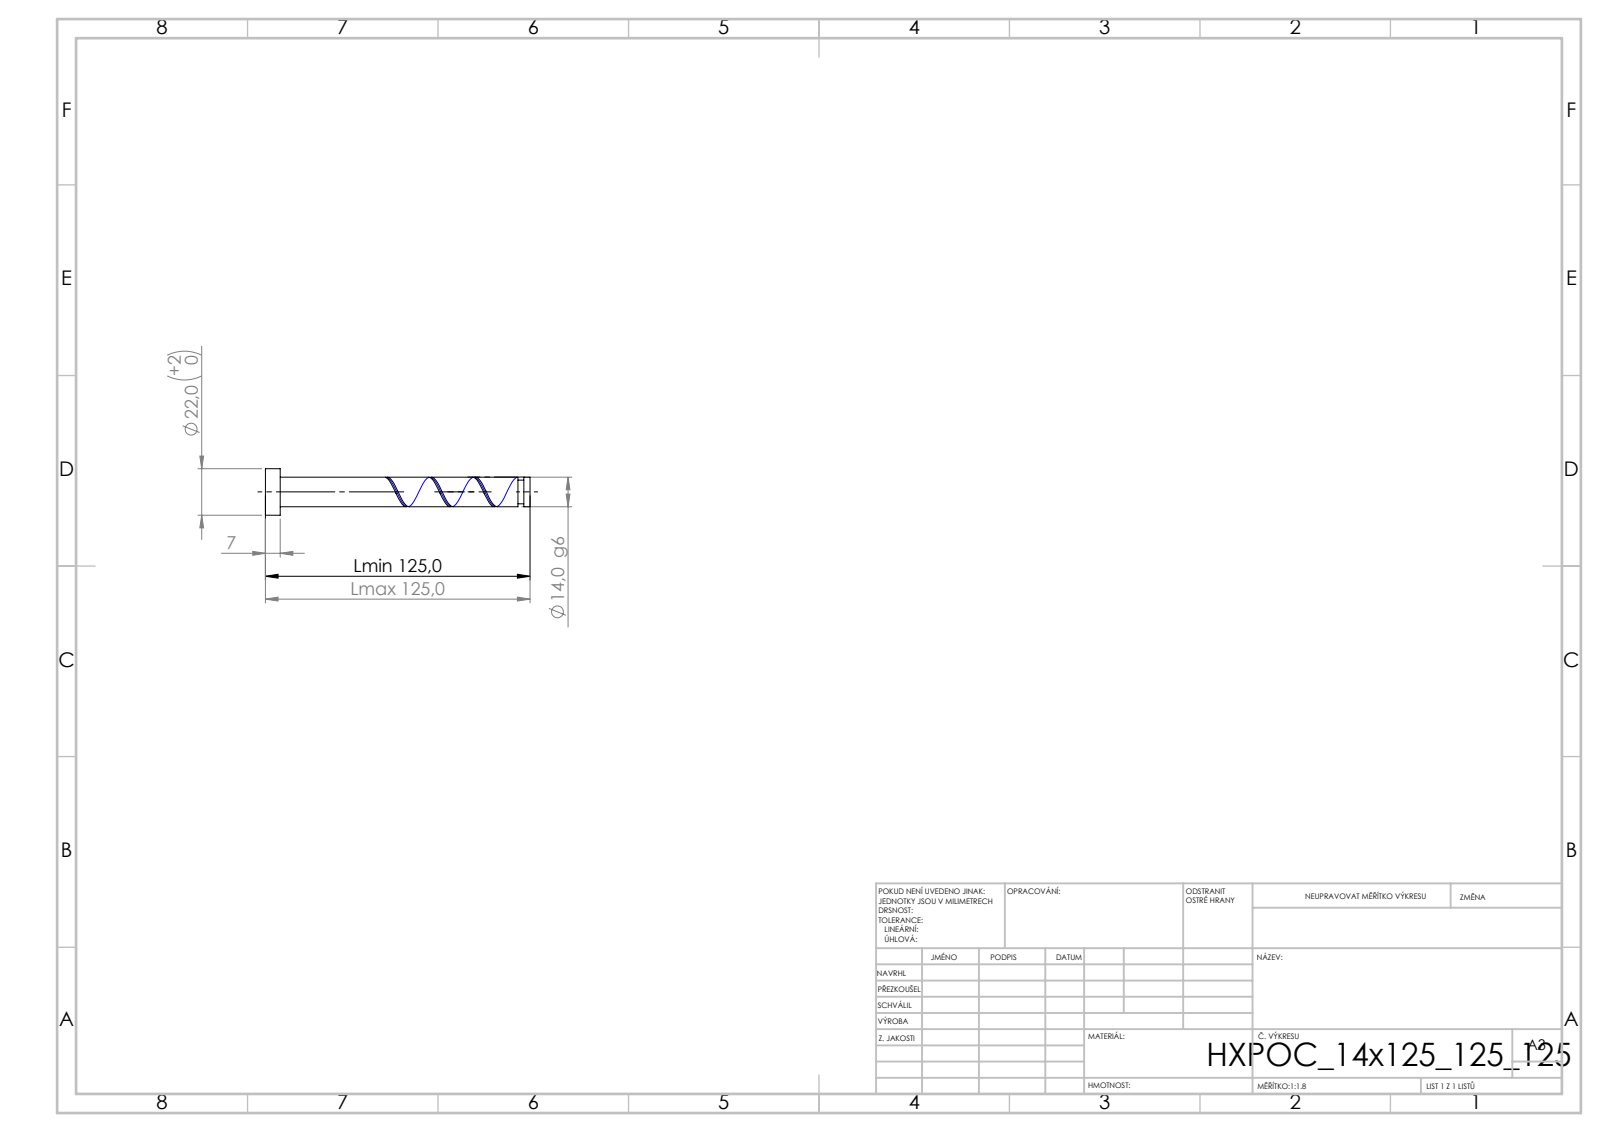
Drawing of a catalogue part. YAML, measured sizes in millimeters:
step_written_by: "SolidWorks 2019 (CONFIG_CONTROL_DESIGN)"
units: millimeters
bodies: {solids: 1, faces: 21, planar: 6, cylindrical: 14, other: 1}
overall_size: [125, 22, 22]
volume: 20486
surface_area: 6781
round_bosses_or_shafts:
  - {diameter: 22, count: 1}
  - {diameter: 14, count: 1}
  - {diameter: 11.2, count: 1}
face_to_face_distances: [7, 125, 118, 122.13, 115.13, 2.87, 119.33, 112.33, 2.8, 5.67]
